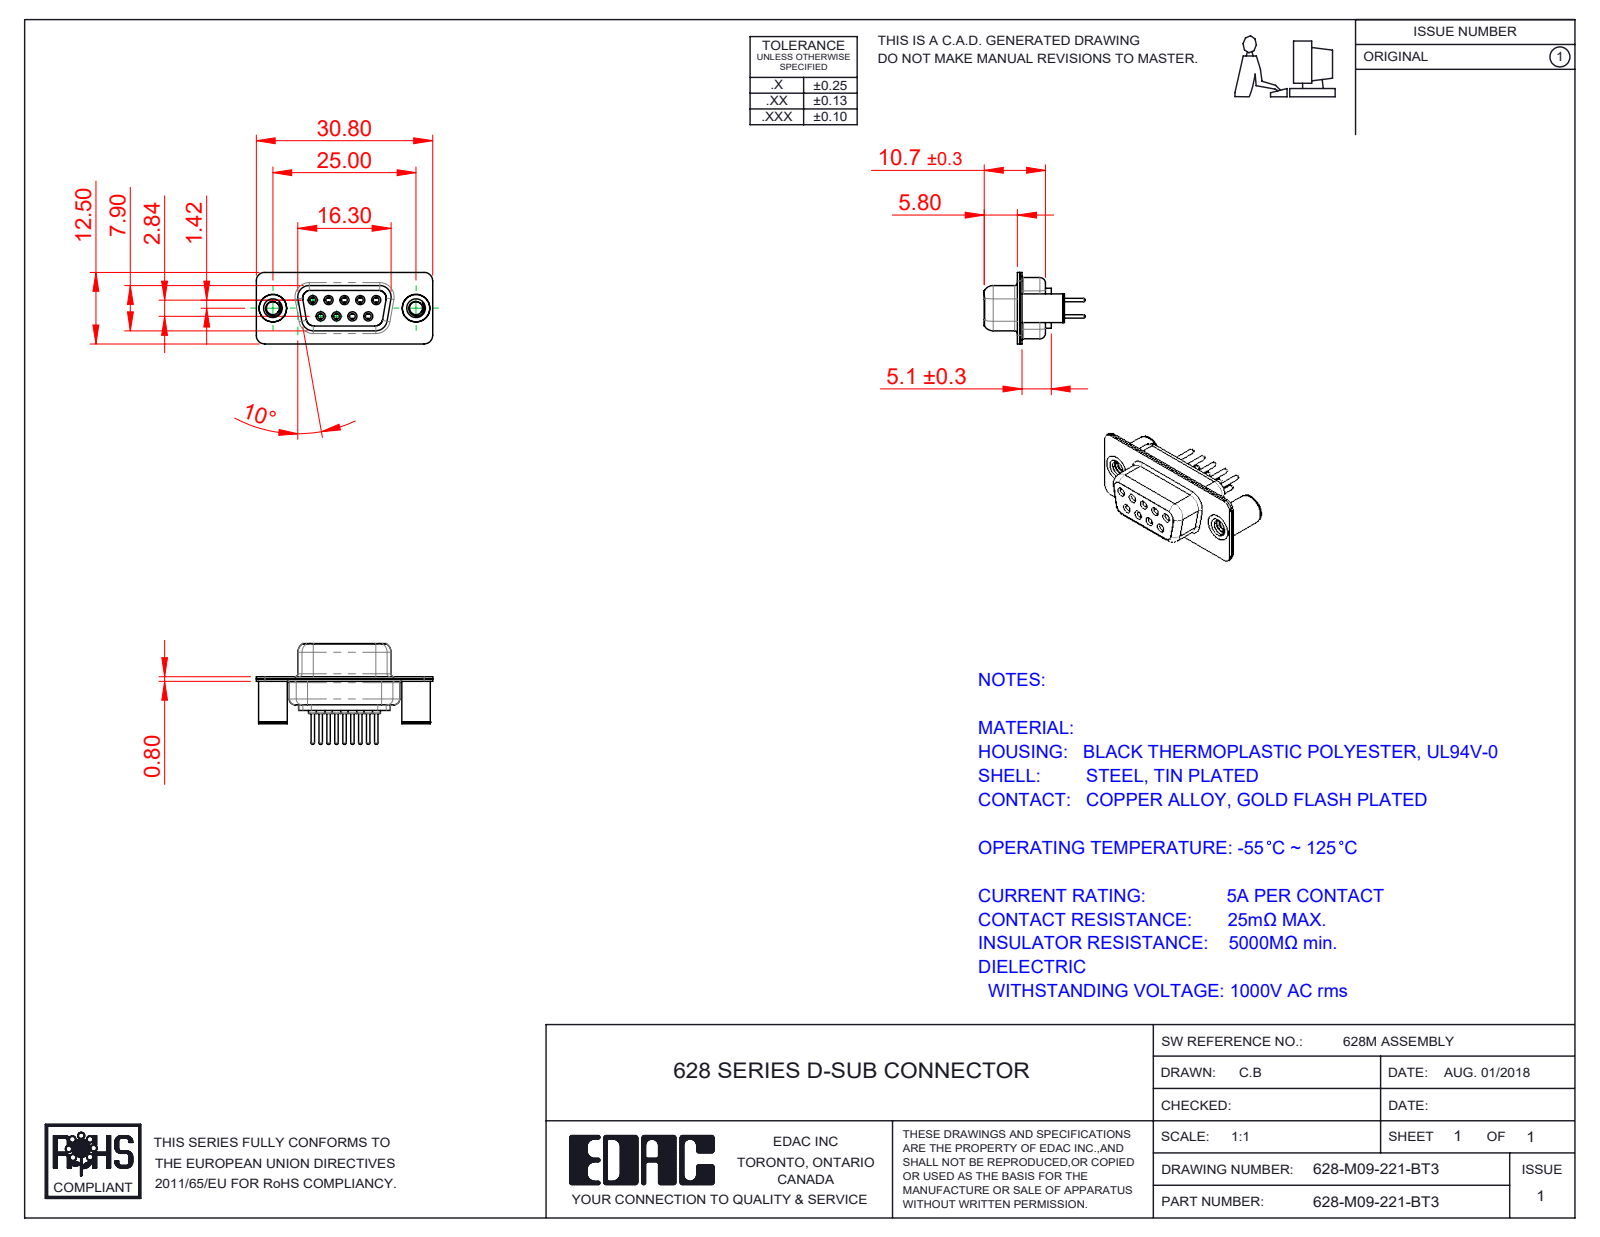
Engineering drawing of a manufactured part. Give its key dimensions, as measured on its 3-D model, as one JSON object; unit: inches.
{"part_name": "628M Contact Row 2_21; 628M Housing_09 Contacts; 628M Contact Row 1_21; 628M Shell Front_09 Contacts (+3 more)", "step_written_by": "SolidWorks 2020 (CONFIG_CONTROL_DESIGN)", "units": "inches", "bodies": {"solids": 14, "faces": 808, "planar": 202, "cylindrical": 332, "other": 274}, "overall_size": [1.213, 0.693, 0.492], "volume_in3": 0.111, "surface_area_in2": 7.256, "round_holes": [[0.039, 9], [0.043, 9], [0.067, 9], [0.071, 9], [0.079, 9], [0.089, 2], [0.128, 2], [0.157, 2], [0.189, 2]], "round_bosses_or_shafts": [[0.087, 9], [0.063, 9], [0.059, 9], [0.024, 9], [0.197, 2], [0.193, 2]], "partial_cylinders_radius": [[0.059, 16], [0.079, 12], [0.053, 8], [0.063, 8], [0.01, 4], [0.02, 4], [0.024, 4], [0.026, 4]], "face_to_face_distances": [0.016, 0.055, 0.018, 0.333, 0.031, 0.071, 0.35, 0.039, 0.244, 0.278], "hole_center_spacings": [0.124, 0.109, 0.218, 0.198, 0.198, 0.327, 0.28, 0.294]}
